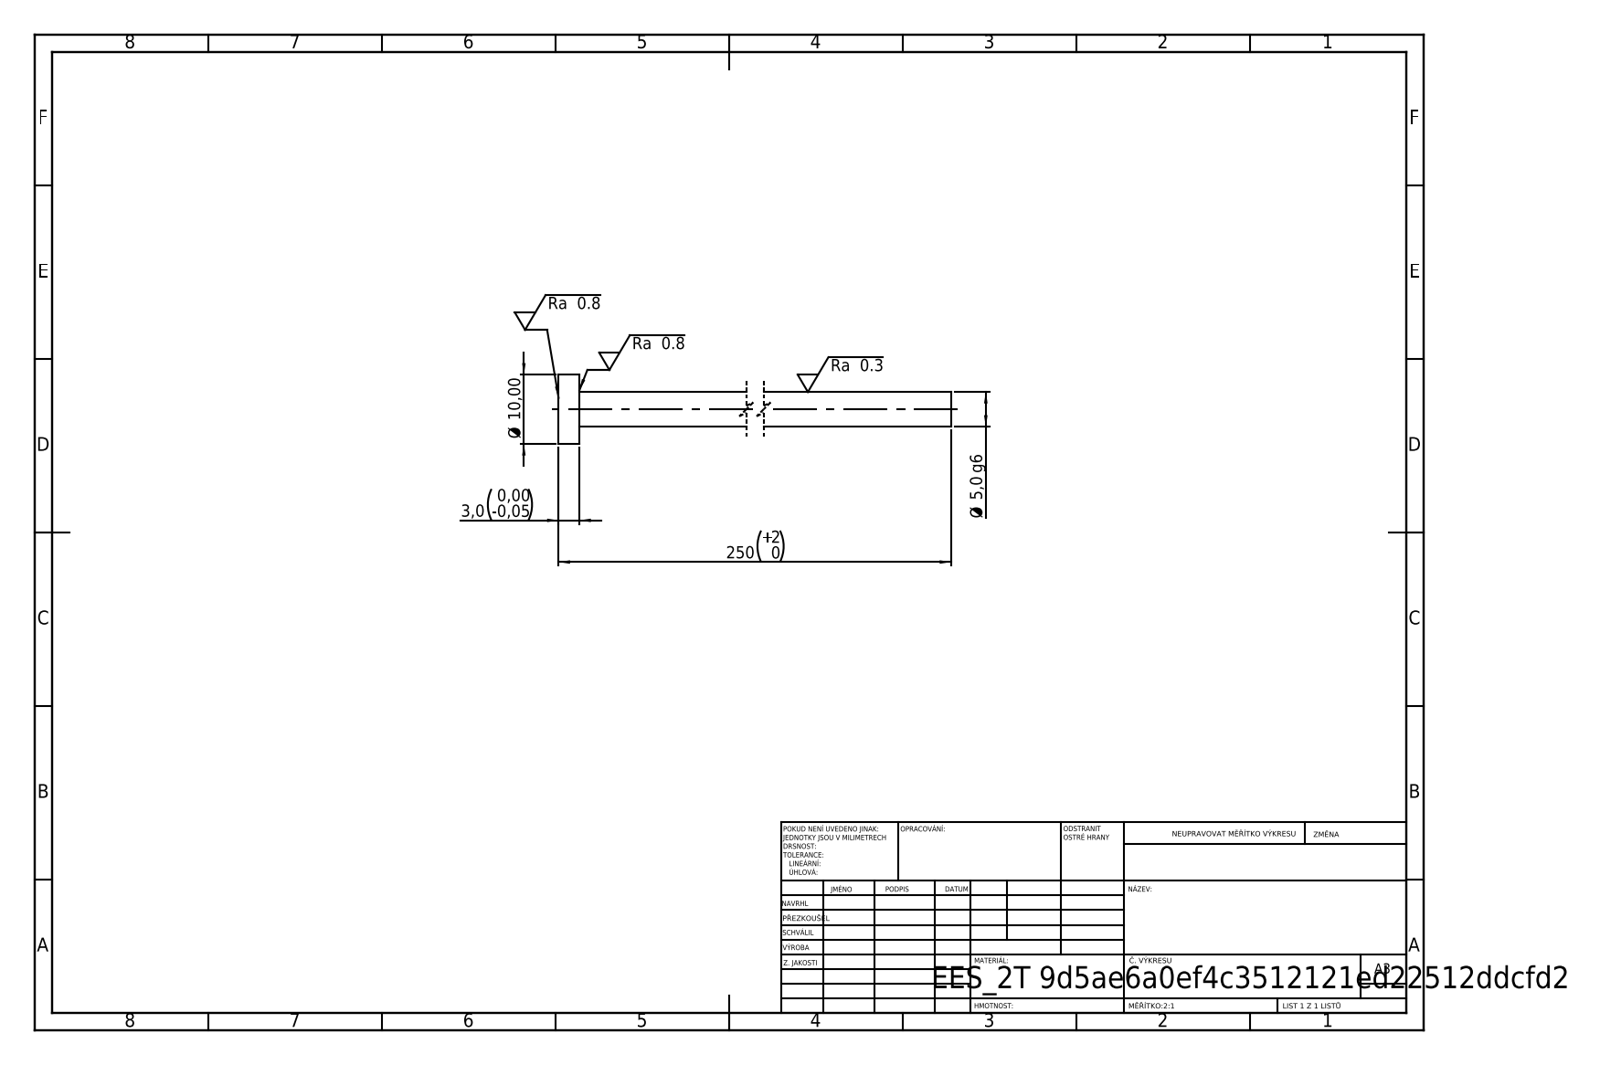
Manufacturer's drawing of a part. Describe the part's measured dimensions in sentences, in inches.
Its 3-D file was written by "SolidWorks 2019 (CONFIG_CONTROL_DESIGN)". It is 1 solid with 7 faces: 3 planar, 4 cylindrical and 0 other. Overall it measures 9.843 by 0.394 by 0.394 inches. Its volume is 0.31 cubic inches and its surface area 6.403 square inches. Round bosses or shafts: 1 of diameter 0.394, 1 of diameter 0.197. The main face-to-face distances are 0.118, 9.843, 9.724.
